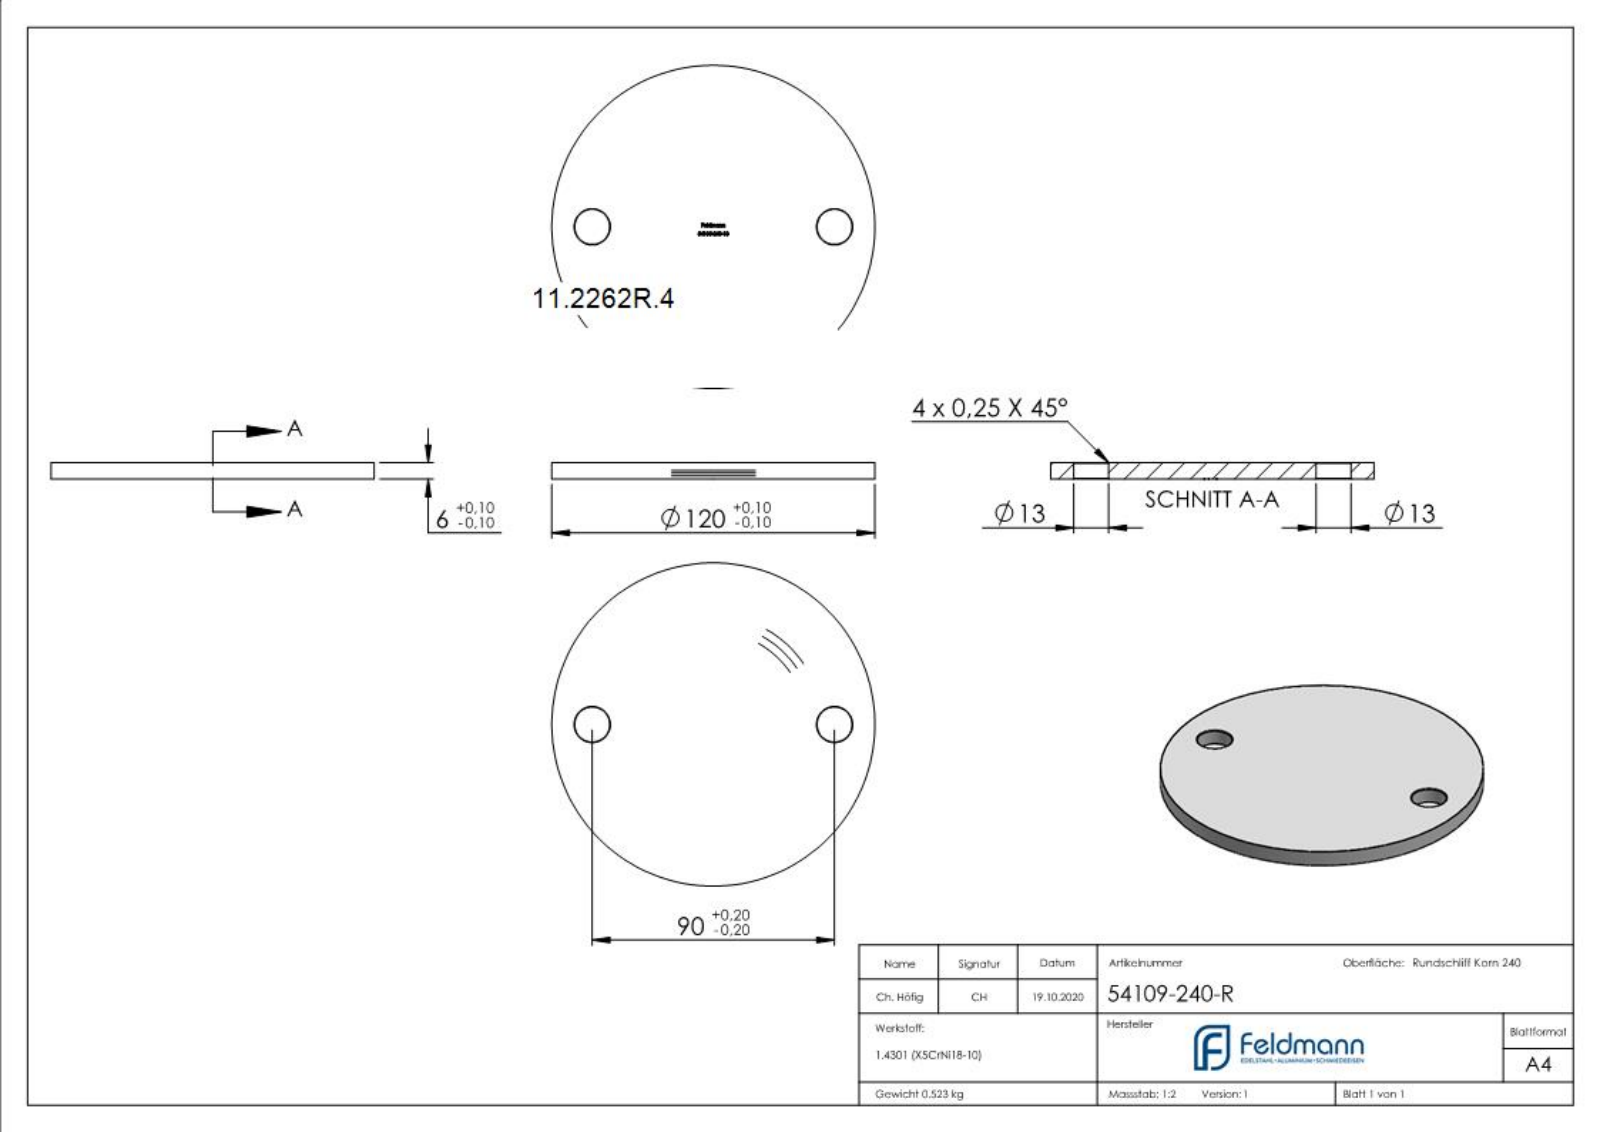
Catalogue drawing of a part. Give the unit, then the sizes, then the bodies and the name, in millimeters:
Units: millimetres
Overall size (bounding box): 120 × 120 × 6
Round holes (diameter × count): ⌀13 ×2
Round bosses / shafts (diameter × count): ⌀120 ×1
Main face-to-face distances: 6, 5.9, 1.53, 2.13, 3.19, 2.02, 6.55, 1.65, 2.97, 8.57
Hole centre spacings: 90
Volume: 66 260 mm³ · Surface area: 24 827 mm²
Bodies: 1 solid, 258 faces (150 planar, 6 cylindrical, 102 other)
Part name (STEP PRODUCT): 54109-240-R
STEP written by: SolidWorks 2018 (CONFIG_CONTROL_DESIGN)
